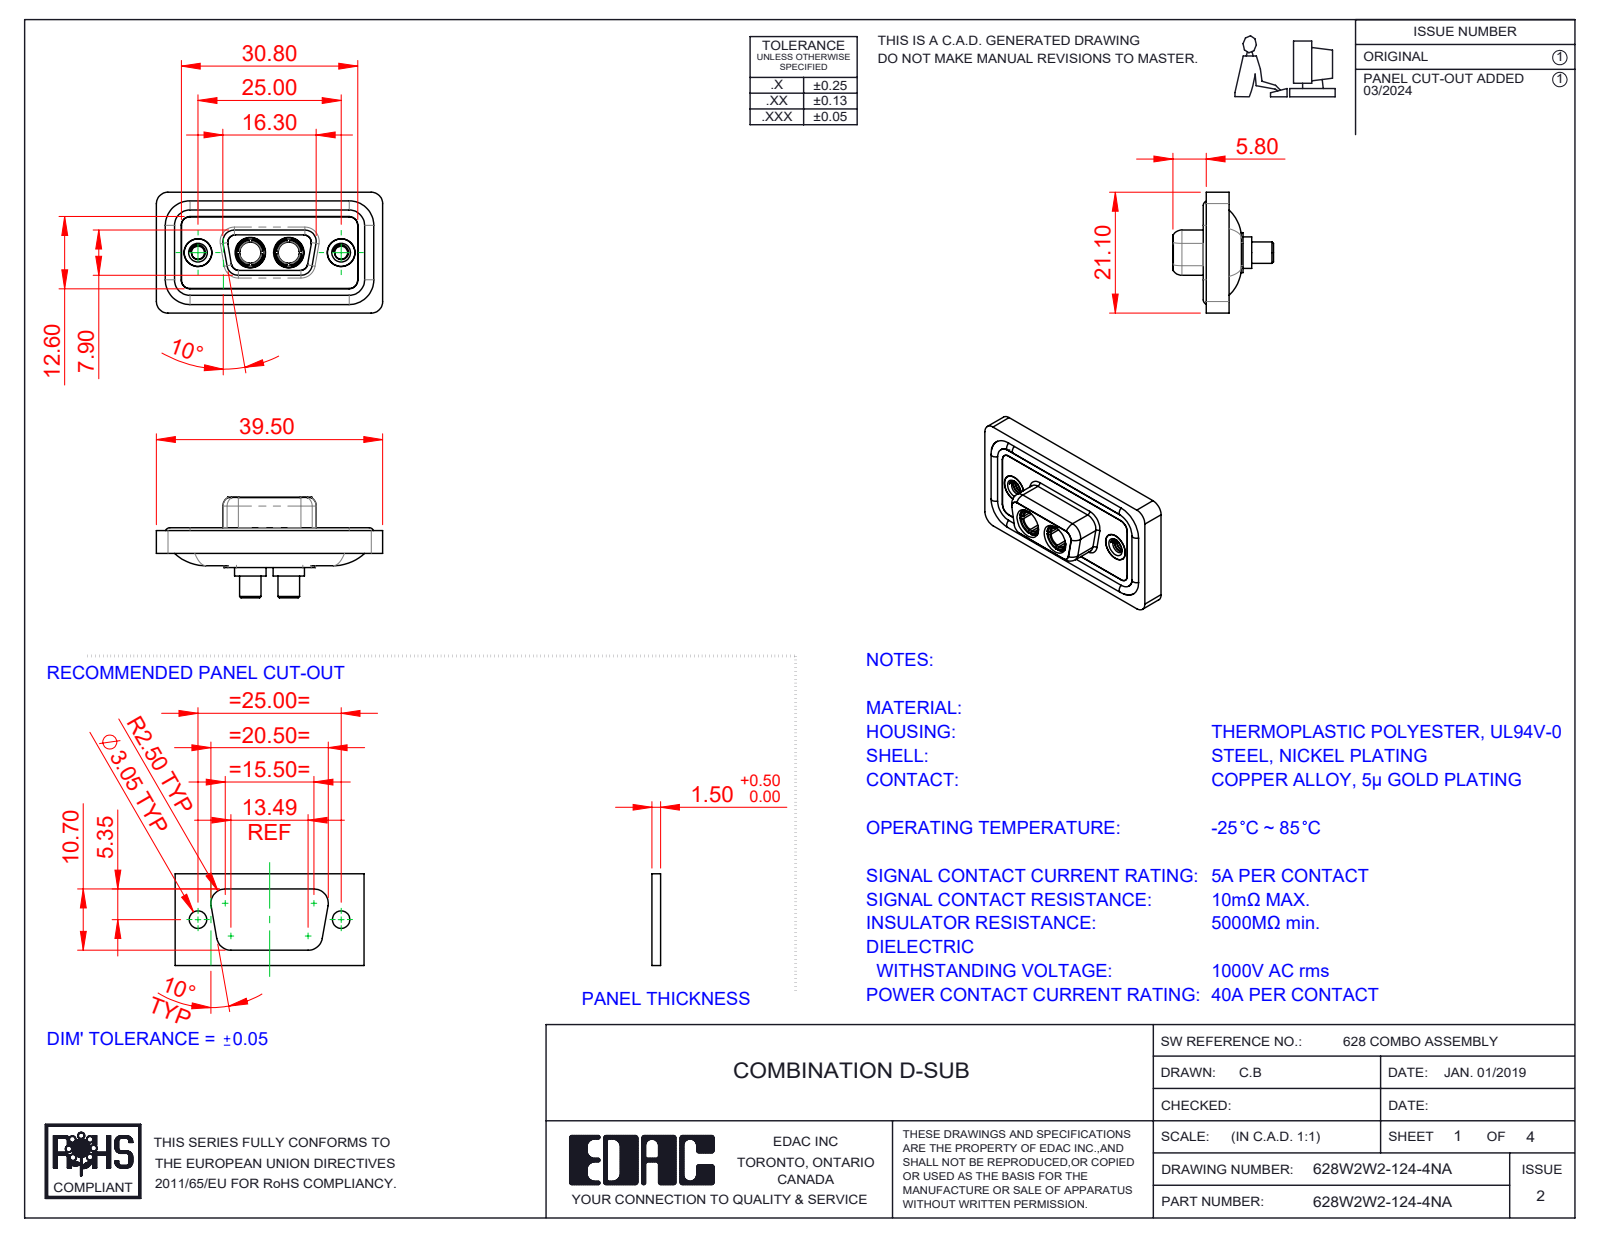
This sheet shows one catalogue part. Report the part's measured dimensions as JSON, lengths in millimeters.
{"part_name": "628Combo Housing_2W2; Power Socket_40A S; 628Combo Shell Rear_09 Contacts; 628Combo Threaded Rivet_A (+3 more)", "step_written_by": "SolidWorks 2023 (CONFIG_CONTROL_DESIGN)", "units": "millimeters", "bodies": {"solids": 11, "faces": 532, "planar": 163, "cylindrical": 236, "other": 133}, "overall_size": [39.5, 21.1, 17.55], "volume_mm3": 4751, "surface_area_mm2": 7655, "round_holes": [[4.85, 4], [2.26, 2], [3.7, 2], [4, 2], [4.05, 2], [5, 2], [5.3, 2]], "round_bosses_or_shafts": [[1.6, 4], [5.5, 2], [5.2, 2], [4.96, 2], [4.95, 2], [4.8, 2], [4.75, 2], [3.75, 2]], "partial_cylinders_radius": [[1.5, 22], [2, 18], [1.35, 8], [1.6, 8], [0.25, 4], [0.5, 4], [0.6, 4], [0.65, 4]], "face_to_face_distances": [0.4, 1.8, 1.1, 2.9, 0.5, 1.6, 5.65, 7.45, 5.35, 3.1], "hole_center_spacings": [9.14, 15.86, 6.72, 25]}
